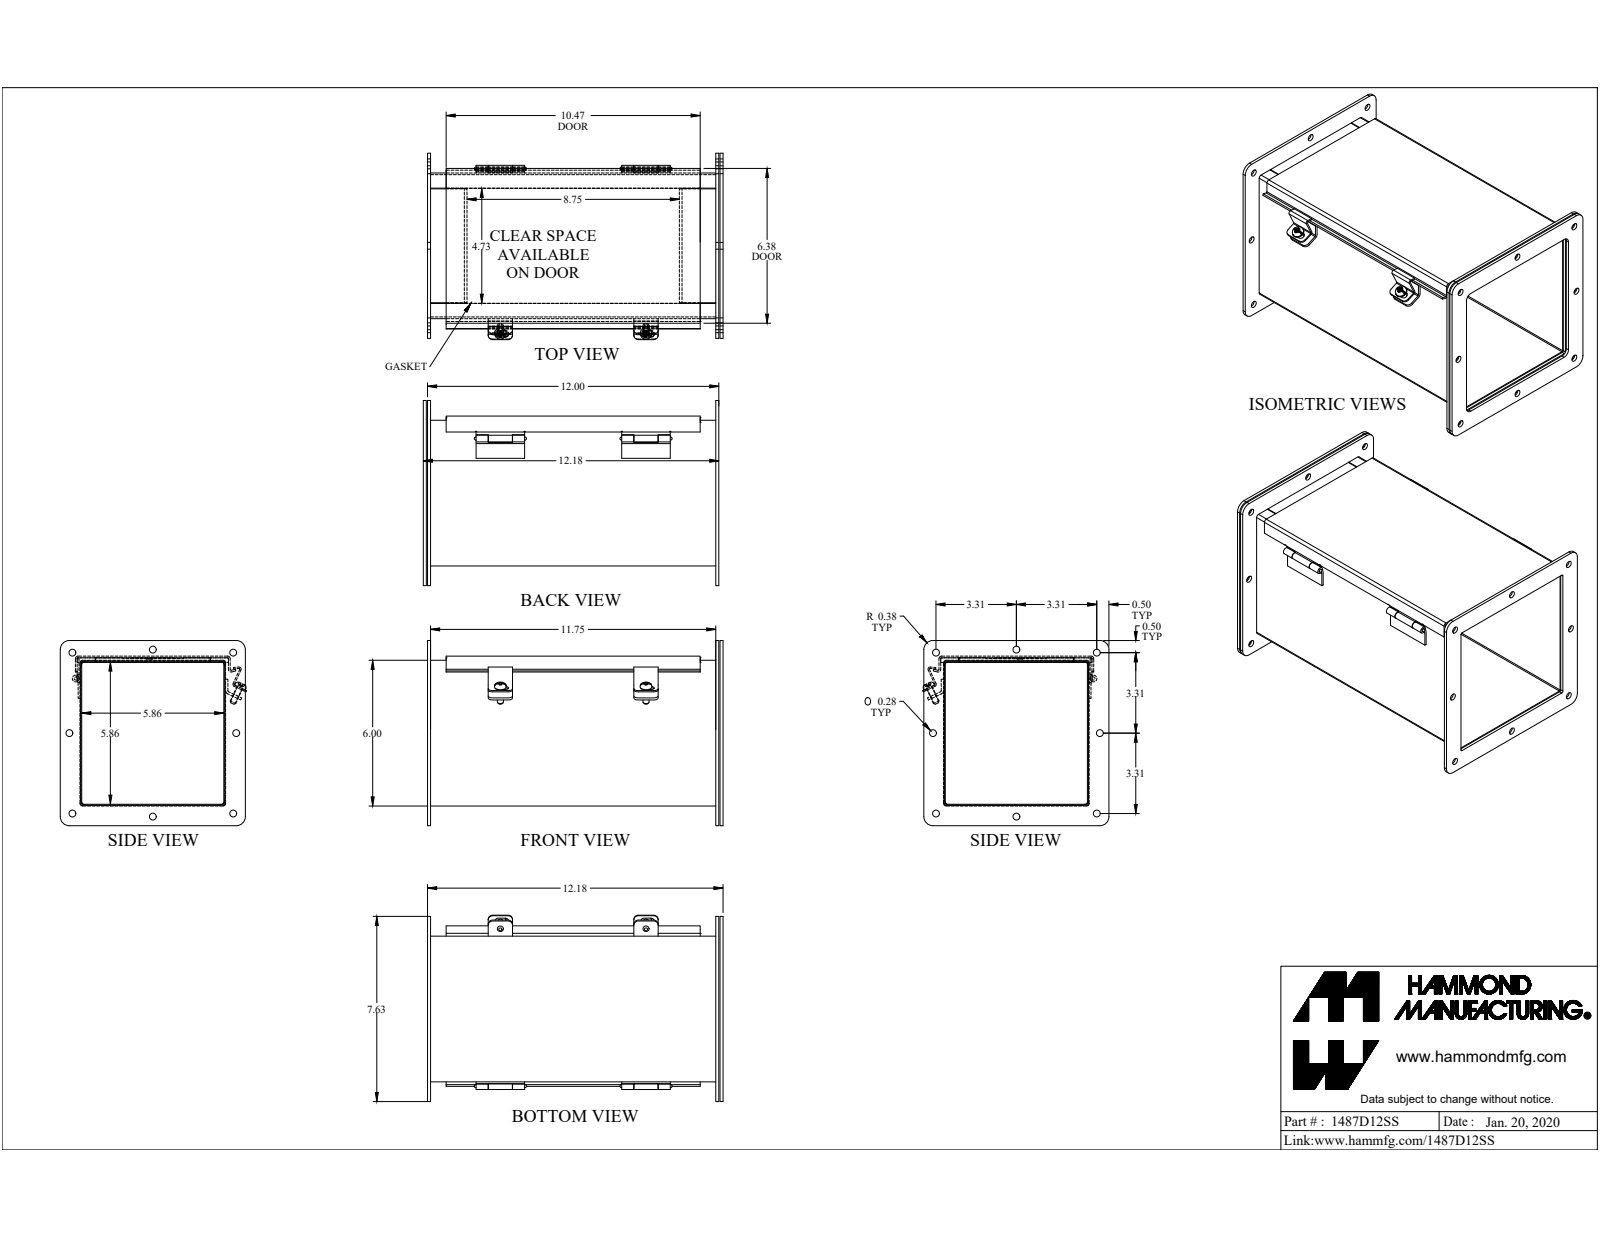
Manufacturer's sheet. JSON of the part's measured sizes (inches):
{"part_name": "1487D12SS", "step_written_by": "SolidWorks 2019 (CONFIG_CONTROL_DESIGN)", "units": "inches", "bodies": {"solids": 27, "faces": 554, "planar": 350, "cylindrical": 152, "other": 52}, "overall_size": [12.546, 7.677, 7.625], "volume_in3": 37, "surface_area_in2": 913.6, "round_holes": [[0.281, 8], [0.213, 2], [0.187, 1], [0.196, 1], [0.258, 1], [0.35, 1]], "round_bosses_or_shafts": [[0.25, 3], [0.48, 2], [0.5, 1], [0.337, 1], [0.18, 1]], "partial_cylinders_radius": [[0.188, 8], [0.375, 8], [0.036, 7], [0.108, 7], [0.02, 6], [0.03, 4], [0.063, 4], [0.141, 4]], "face_to_face_distances": [0.072, 5.928, 6.1, 6, 5.856, 6.028, 0.125, 6.172, 0.172, 0.175], "hole_center_spacings": [7.519, 3.315, 3.315, 4.861, 4.861, 6.625, 6.625, 9.369]}
